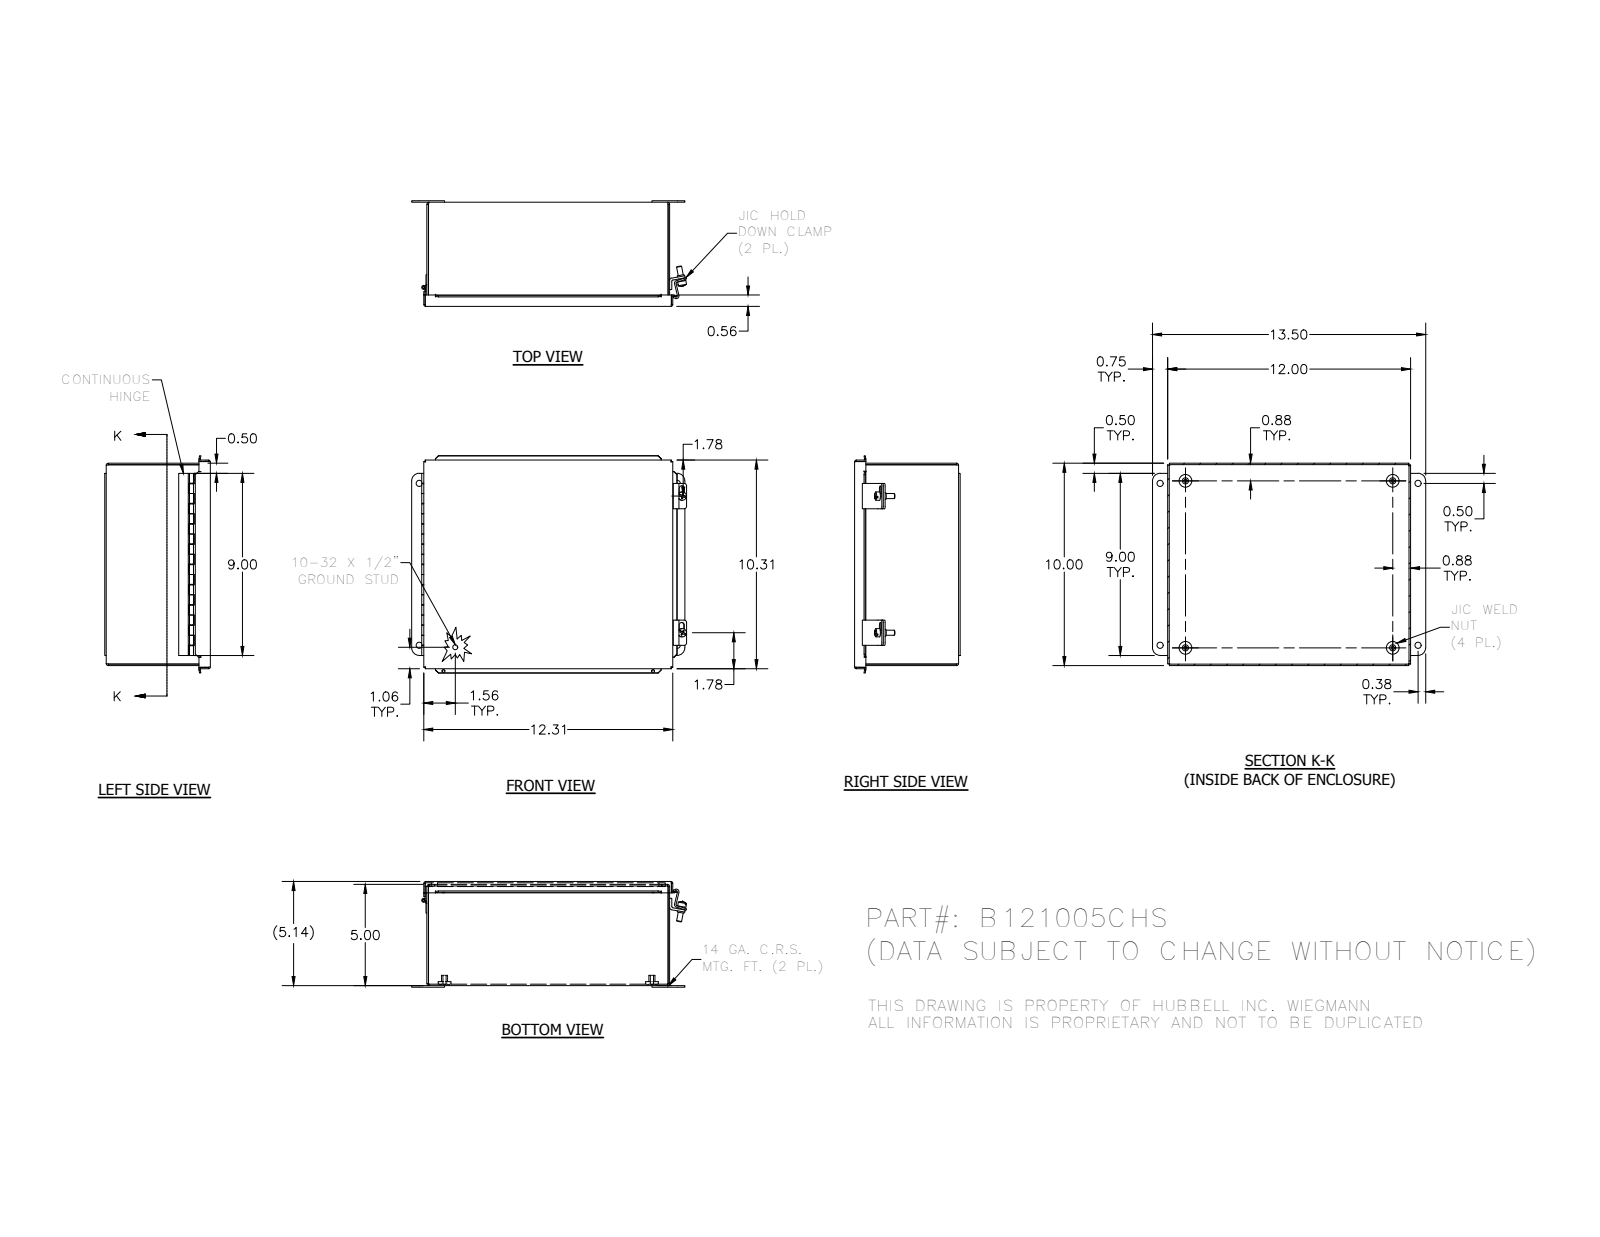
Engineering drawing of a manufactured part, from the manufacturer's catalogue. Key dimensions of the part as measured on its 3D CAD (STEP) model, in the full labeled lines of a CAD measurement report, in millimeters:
Part name (STEP PRODUCT): B121005CHS; 3499; 3484; C1001 (+8 more)
STEP written by: Autodesk Inventor 2012 (AUTOMOTIVE_DESIGN)
Units: millimetres
Bodies: 20 solids, 479 faces (311 planar, 123 cylindrical, 45 other)
Overall size (bounding box): 345.1 × 272.8 × 132.6
Volume: 718 900 mm³ · Surface area: 773 500 mm²
Round holes (diameter × count): ⌀4 ×4, ⌀7.9 ×4, ⌀3.6 ×2, ⌀5 ×2, ⌀2.9 ×1
Round bosses / shafts (diameter × count): ⌀15.9 ×4, ⌀7.6 ×4, ⌀6.4 ×3, ⌀10.4 ×2, ⌀8.7 ×2, ⌀5.1 ×1, ⌀4.8 ×1, ⌀2.5 ×1
Partial cylindrical surfaces — rounded edges, fillets, slot ends (radius × count): R0.8 ×15, R2.7 ×8, R3.2 ×8, R2.4 ×7, R3.4 ×4, R9.5 ×4, R1.6 ×3, R3.2 ×3
Main face-to-face distances: 1.9, 129.1, 130.7, 1.6, 127.2, 128.8, 252.1, 302.9, 254, 250.2
Hole centre spacings: 31.9, 208.8, 292.1, 357.7, 203.2, 323.9, 334.2, 382.3
